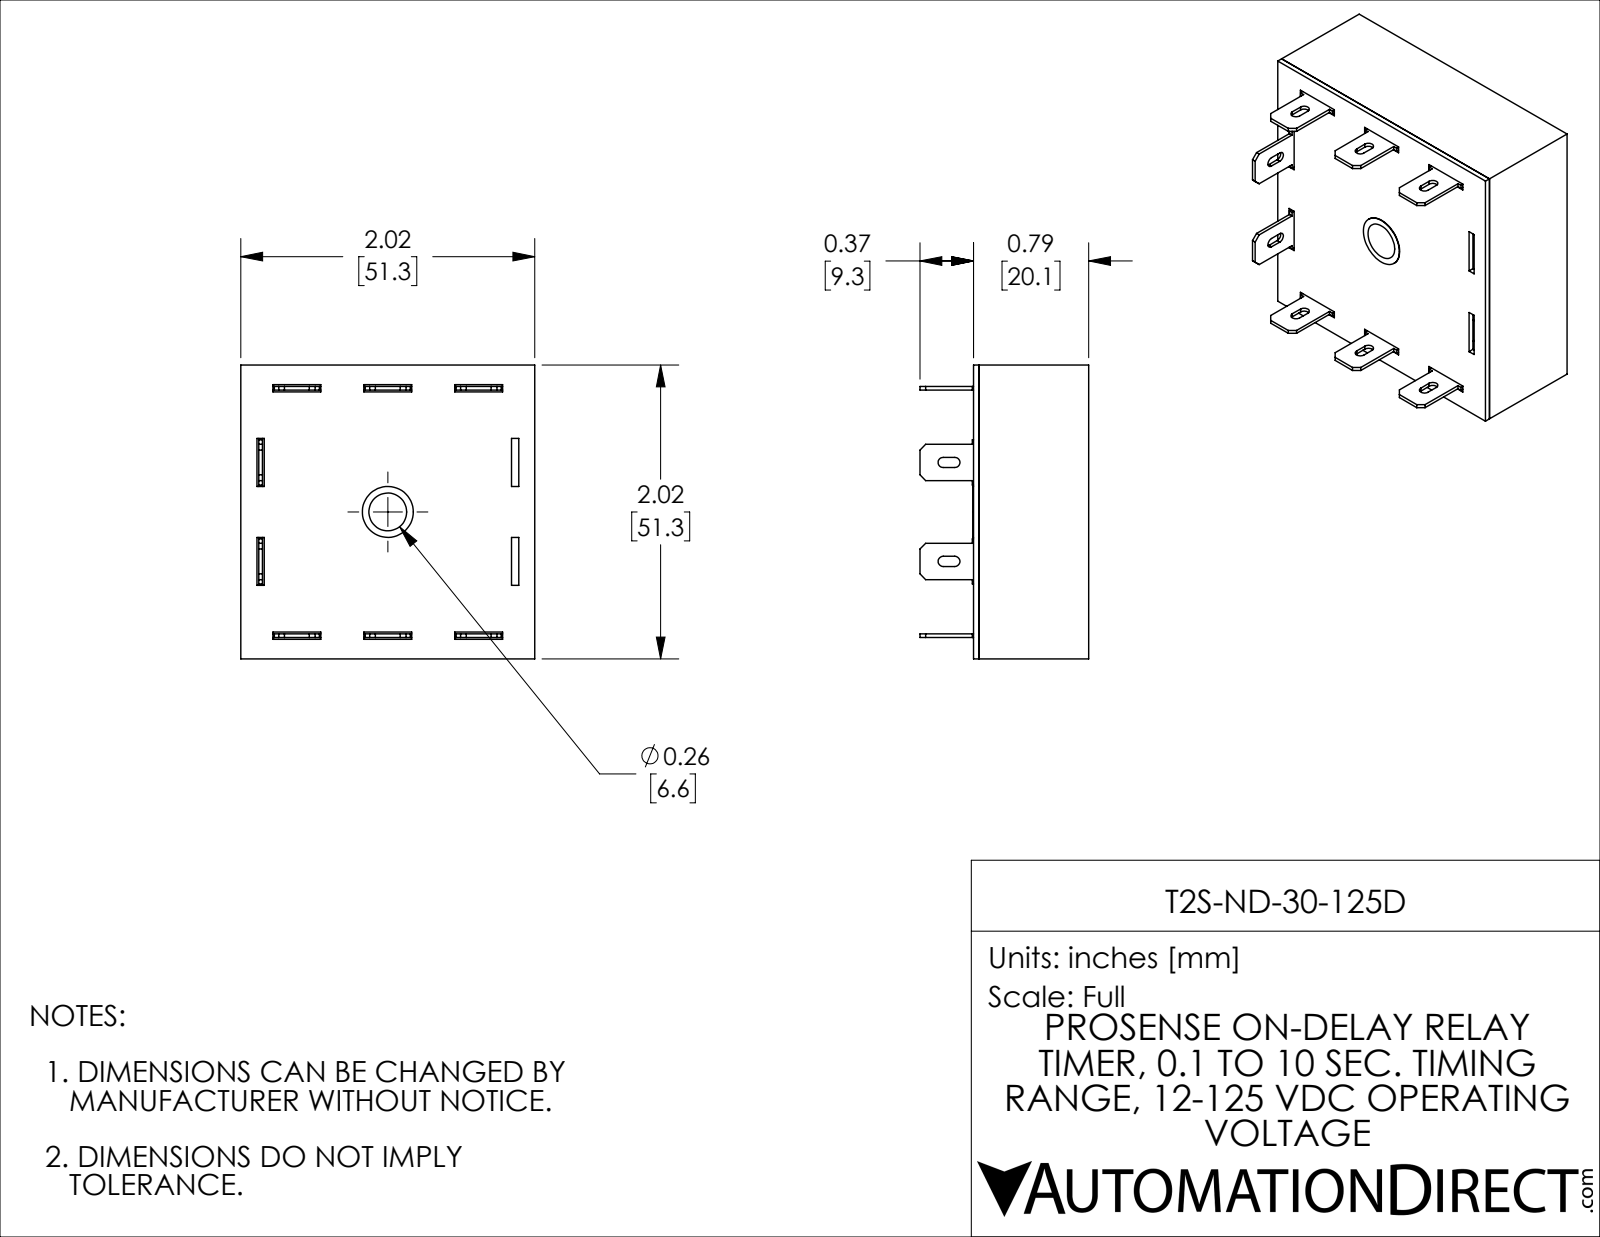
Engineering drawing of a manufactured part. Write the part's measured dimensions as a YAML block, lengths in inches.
part_name: "T2S-ND-30-125D"
step_written_by: "SolidWorks 2021 (CONFIG_CONTROL_DESIGN)"
units: inches
bodies: {solids: 10, faces: 256, planar: 234, cylindrical: 20, other: 2}
overall_size: [2.02, 2.02, 1.16]
volume: 0.674
surface_area: 35.37
round_holes:
  - {diameter: 0.35, count: 1}
partial_cylinders:
  - {radius: 0.035, count: 10}
face_to_face_distances: [0.045, 1.975, 0.754, 0.792, 0.038, 0.709, 0.747, 2.02, 1.93, 0.147]
